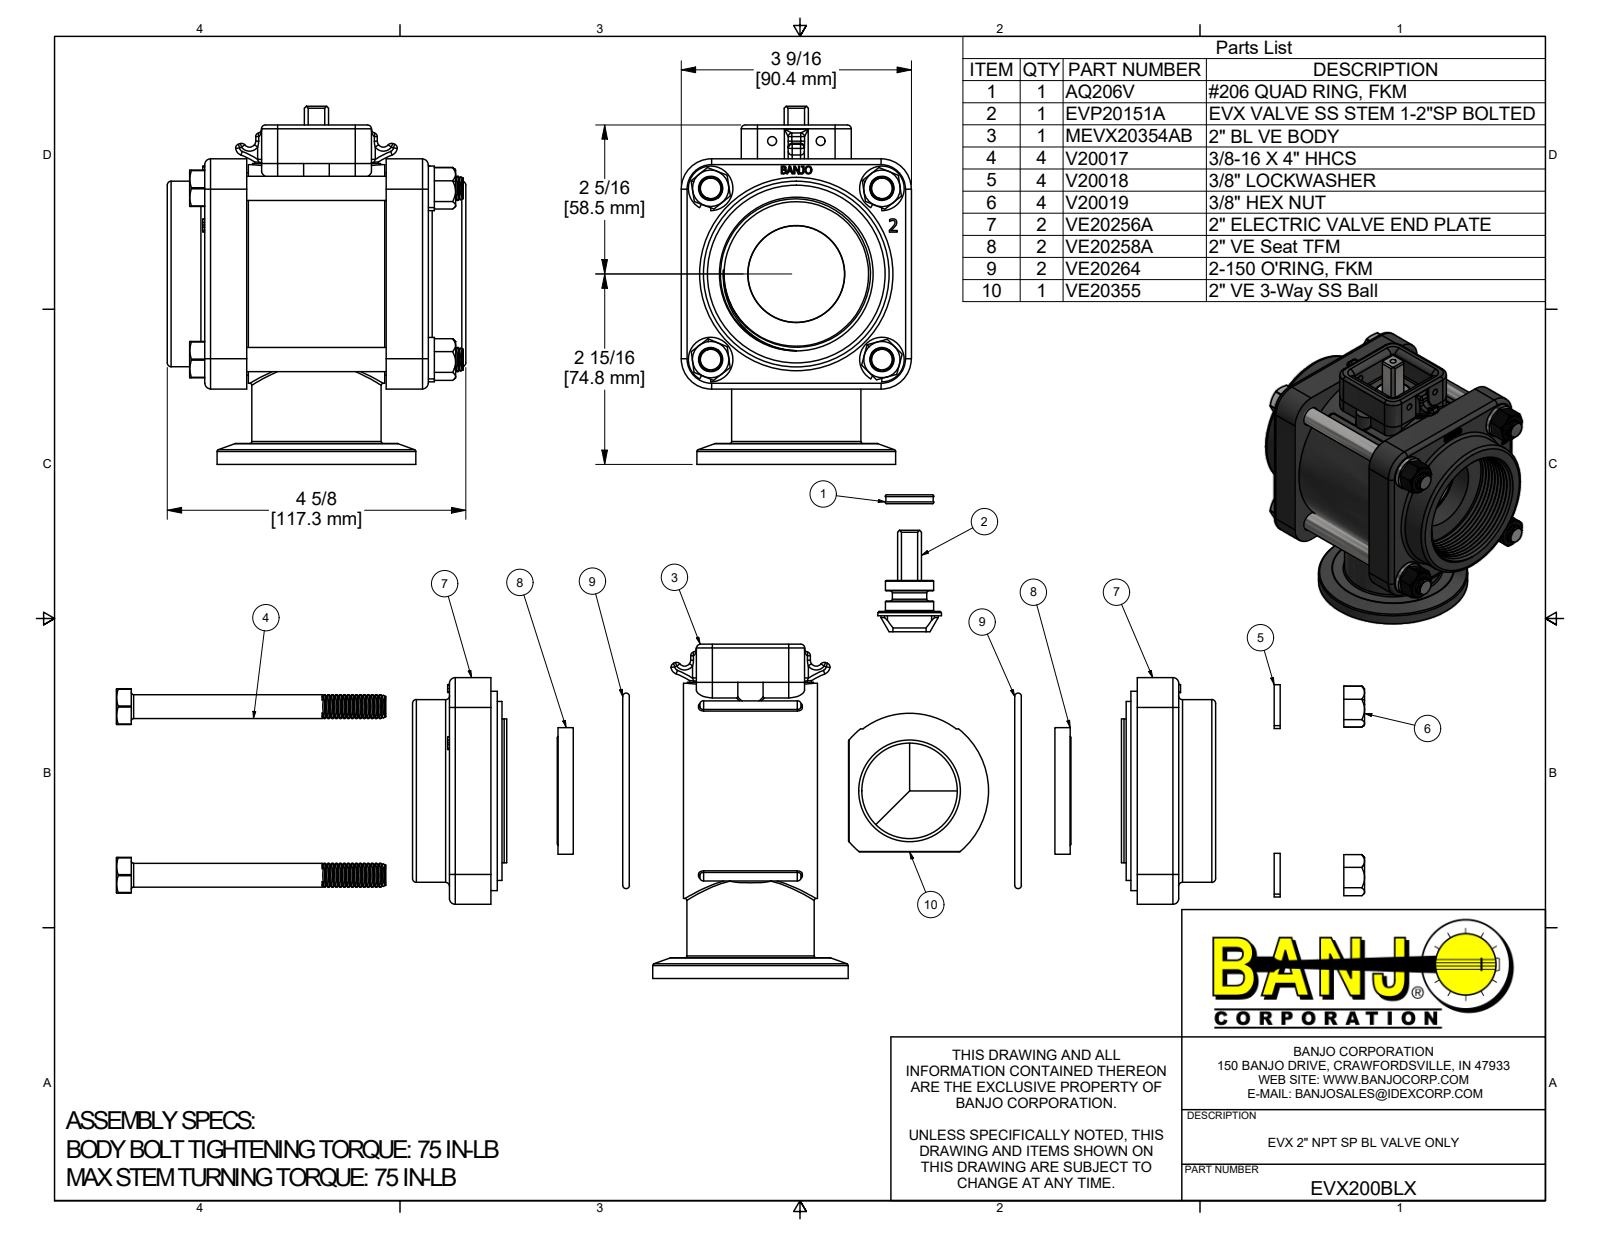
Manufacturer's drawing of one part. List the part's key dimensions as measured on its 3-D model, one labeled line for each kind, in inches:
Part name (STEP PRODUCT): EVX200BLX; MEVX20354AB; MEVX20354ABX; V20017 (+8 more)
STEP written by: Autodesk Inventor 2019 (AUTOMOTIVE_DESIGN)
Units: inches
Bodies: 22 solids, 1296 faces (340 planar, 405 cylindrical, 551 other)
Overall size (bounding box): 5.538 × 4.618 × 3.56
Volume: 32.75 in³ · Surface area: 270.5 in²
Round holes (diameter × count): ⌀0.307 ×4, ⌀0.385 ×4, ⌀0.406 ×4, ⌀1.5 ×3, ⌀0.135 ×2, ⌀0.76 ×1, ⌀1.02 ×1, ⌀1.48 ×1, ⌀1.495 ×1, ⌀1.995 ×1, ⌀2.185 ×1, ⌀2.236 ×1
Round bosses / shafts (diameter × count): ⌀0.324 ×60, ⌀0.687 ×4, ⌀0.375 ×4, ⌀3.38 ×1, ⌀3.13 ×1, ⌀3.074 ×1, ⌀2.87 ×1, ⌀2.812 ×1
Partial cylindrical surfaces — rounded edges, fillets, slot ends (radius × count): R0.06 ×28, R0.09 ×12, R0.02 ×8, R0.162 ×8, R0.125 ×6, R0.015 ×4, R0.03 ×4, R0.21 ×4
Main face-to-face distances: 0.65, 2.808, 0.825, 2.633, 0.175, 1.983, 3.56, 0.1, 0.37, 0.28
Hole centre spacings: 1.872, 2.648, 1.198, 1.849, 2.088, 3.509, 3.745, 3.781
